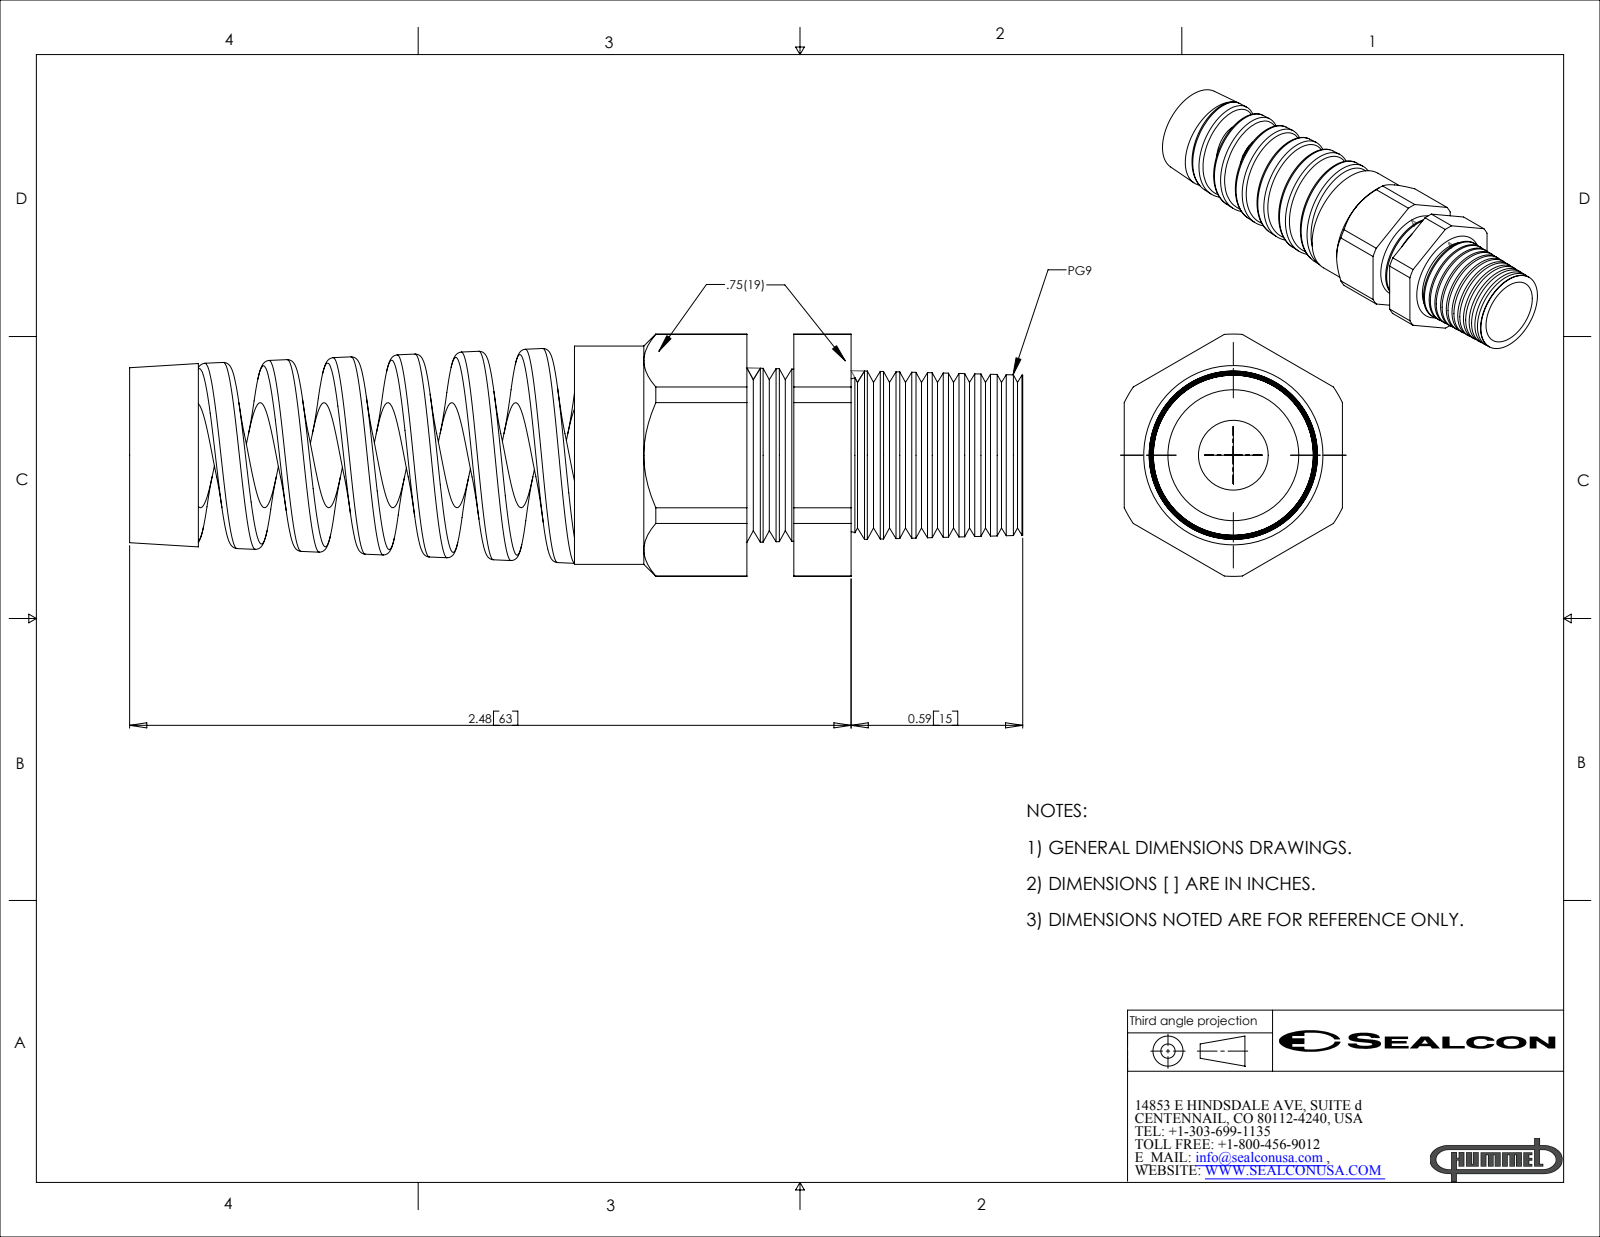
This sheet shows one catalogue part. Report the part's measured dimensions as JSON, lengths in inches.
{"part_name": "CF09CR-GY", "step_written_by": "SolidWorks 2007 (CONFIG_CONTROL_DESIGN)", "units": "inches", "bodies": {"solids": 2, "faces": 182, "planar": 24, "cylindrical": 38, "other": 120}, "overall_size": [3.07, 0.833, 0.75], "volume_in3": 0.643, "surface_area_in2": 13.44, "round_holes": [[0.24, 1], [0.361, 1], [0.39, 1]], "round_bosses_or_shafts": [[0.75, 1], [0.45, 1]], "partial_cylinders_radius": [[0.416, 1]], "face_to_face_distances": [0.75, 0.161, 0.75, 0.354, 0.516, 0.713, 0.358, 0.197, 0.239, 0.593]}
